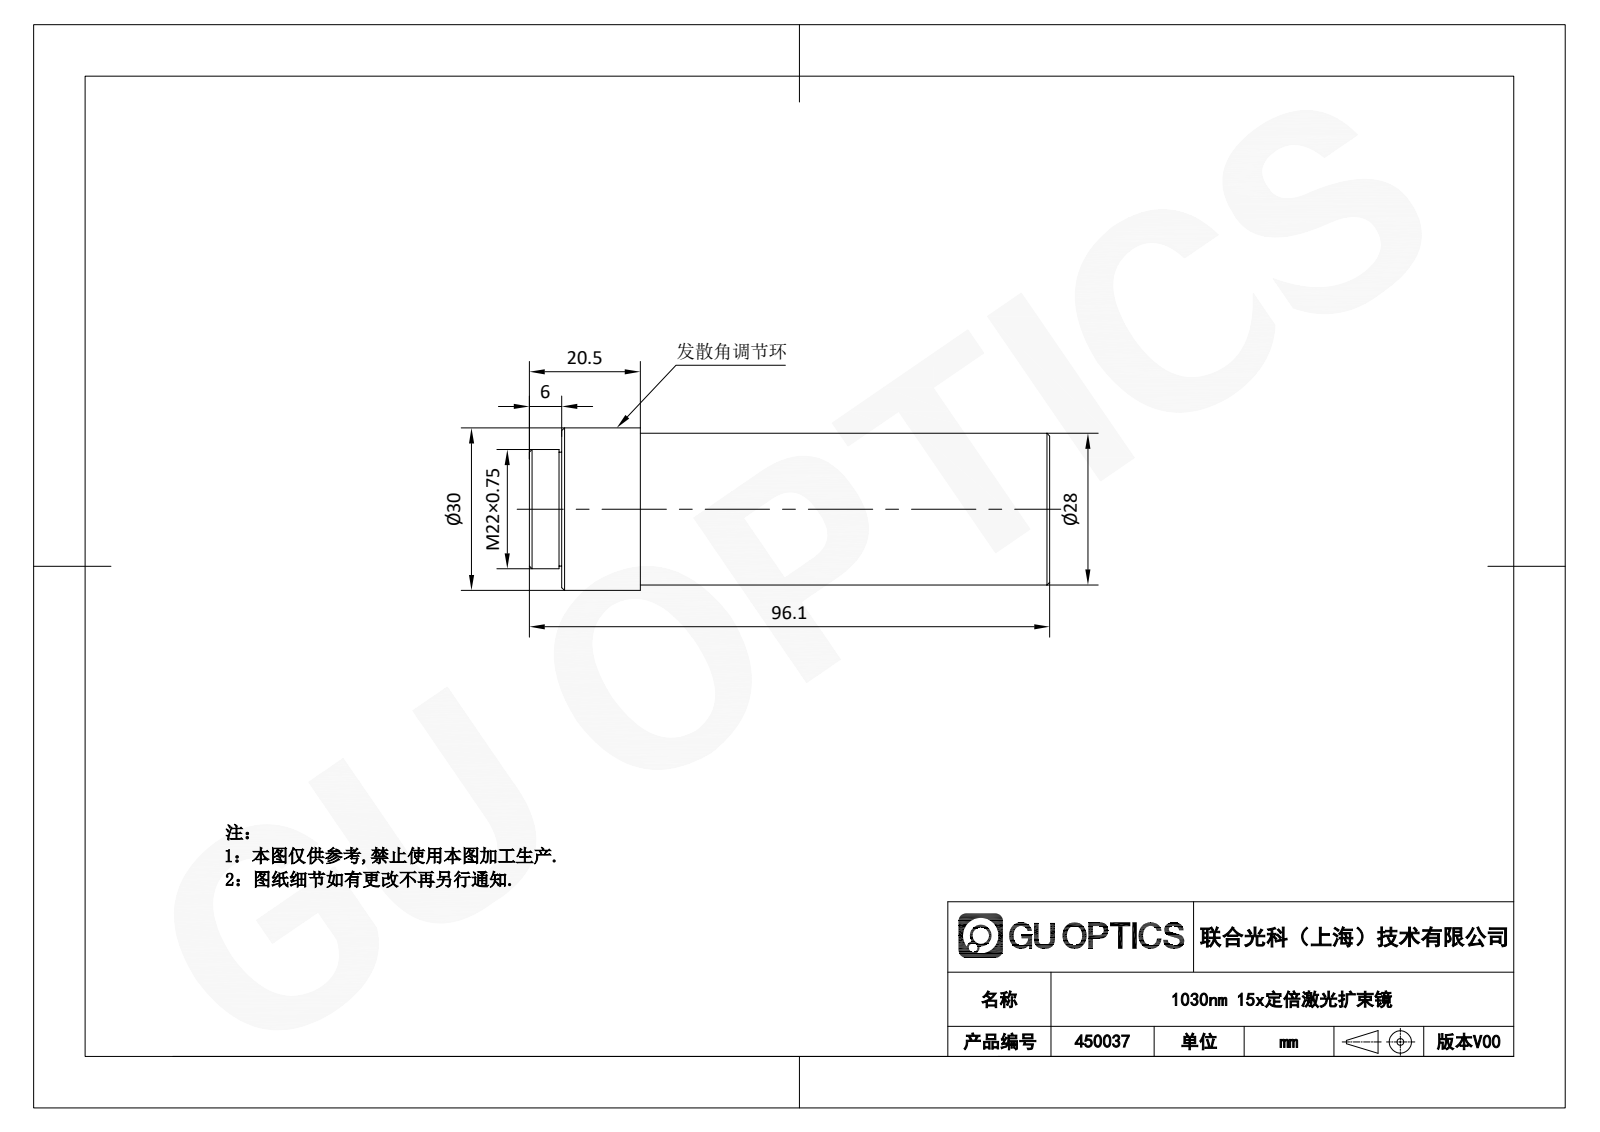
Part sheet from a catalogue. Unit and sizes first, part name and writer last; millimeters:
Units: millimetres
Overall size (bounding box): 96.1 × 30 × 30
Round holes (diameter × count): ⌀18 ×1
Round bosses / shafts (diameter × count): ⌀30 ×1, ⌀28 ×1, ⌀22 ×1, ⌀21 ×1
Main face-to-face distances: 96.1, 6, 90.1, 94.1, 88.1, 2, 20.5, 14.5, 73.6, 75.6
Volume: 58 524 mm³ · Surface area: 9 950 mm²
Bodies: 1 solid, 22 faces (6 planar, 10 cylindrical, 6 other)
Part name (STEP PRODUCT): 450037
STEP written by: SolidWorks 2020 (CONFIG_CONTROL_DESIGN)
